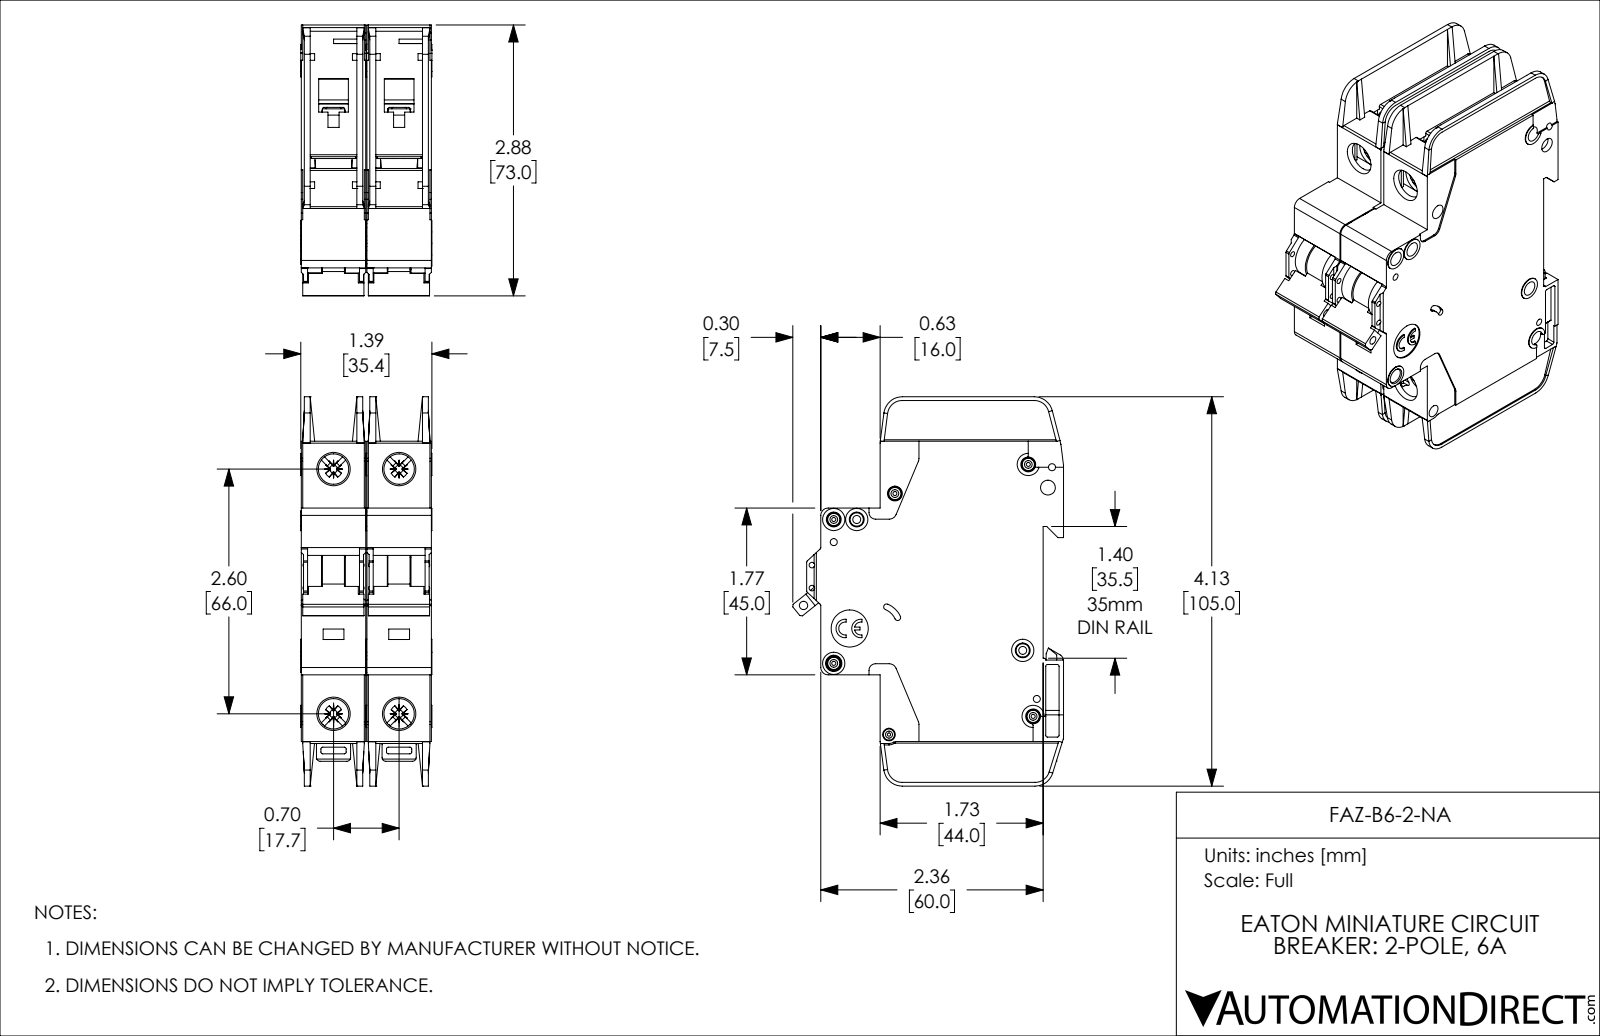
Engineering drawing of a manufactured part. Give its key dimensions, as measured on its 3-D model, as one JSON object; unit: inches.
{"part_name": "FAZ-B6-2-NA", "step_written_by": "SolidWorks 2019 (AUTOMOTIVE_DESIGN)", "units": "inches", "bodies": {"solids": 2, "faces": 2254, "planar": 1342, "cylindrical": 714, "other": 198}, "overall_size": [4.134, 2.876, 1.394], "volume_in3": 9.365, "surface_area_in2": 82.01, "round_holes": [[0.157, 8], [0.043, 5], [0.075, 4], [0.323, 4], [0.059, 2], [0.085, 2], [0.035, 1], [0.089, 1], [0.098, 1], [0.134, 1], [0.394, 1]], "round_bosses_or_shafts": [[0.13, 5], [0.236, 4], [0.118, 3], [0.098, 2]], "partial_cylinders_radius": [[0.02, 57], [0.016, 20], [0.039, 14], [0.079, 10], [0.043, 8], [0.008, 5], [0.197, 5], [0.01, 4]], "face_to_face_distances": [0.697, 0.047, 0.685, 0.591, 0.094, 0.638, 0.543, 1.382, 0.744, 0.65], "hole_center_spacings": [0.244, 0.537, 0.697, 0.87, 2.598, 2.69, 0.189, 0.199]}
